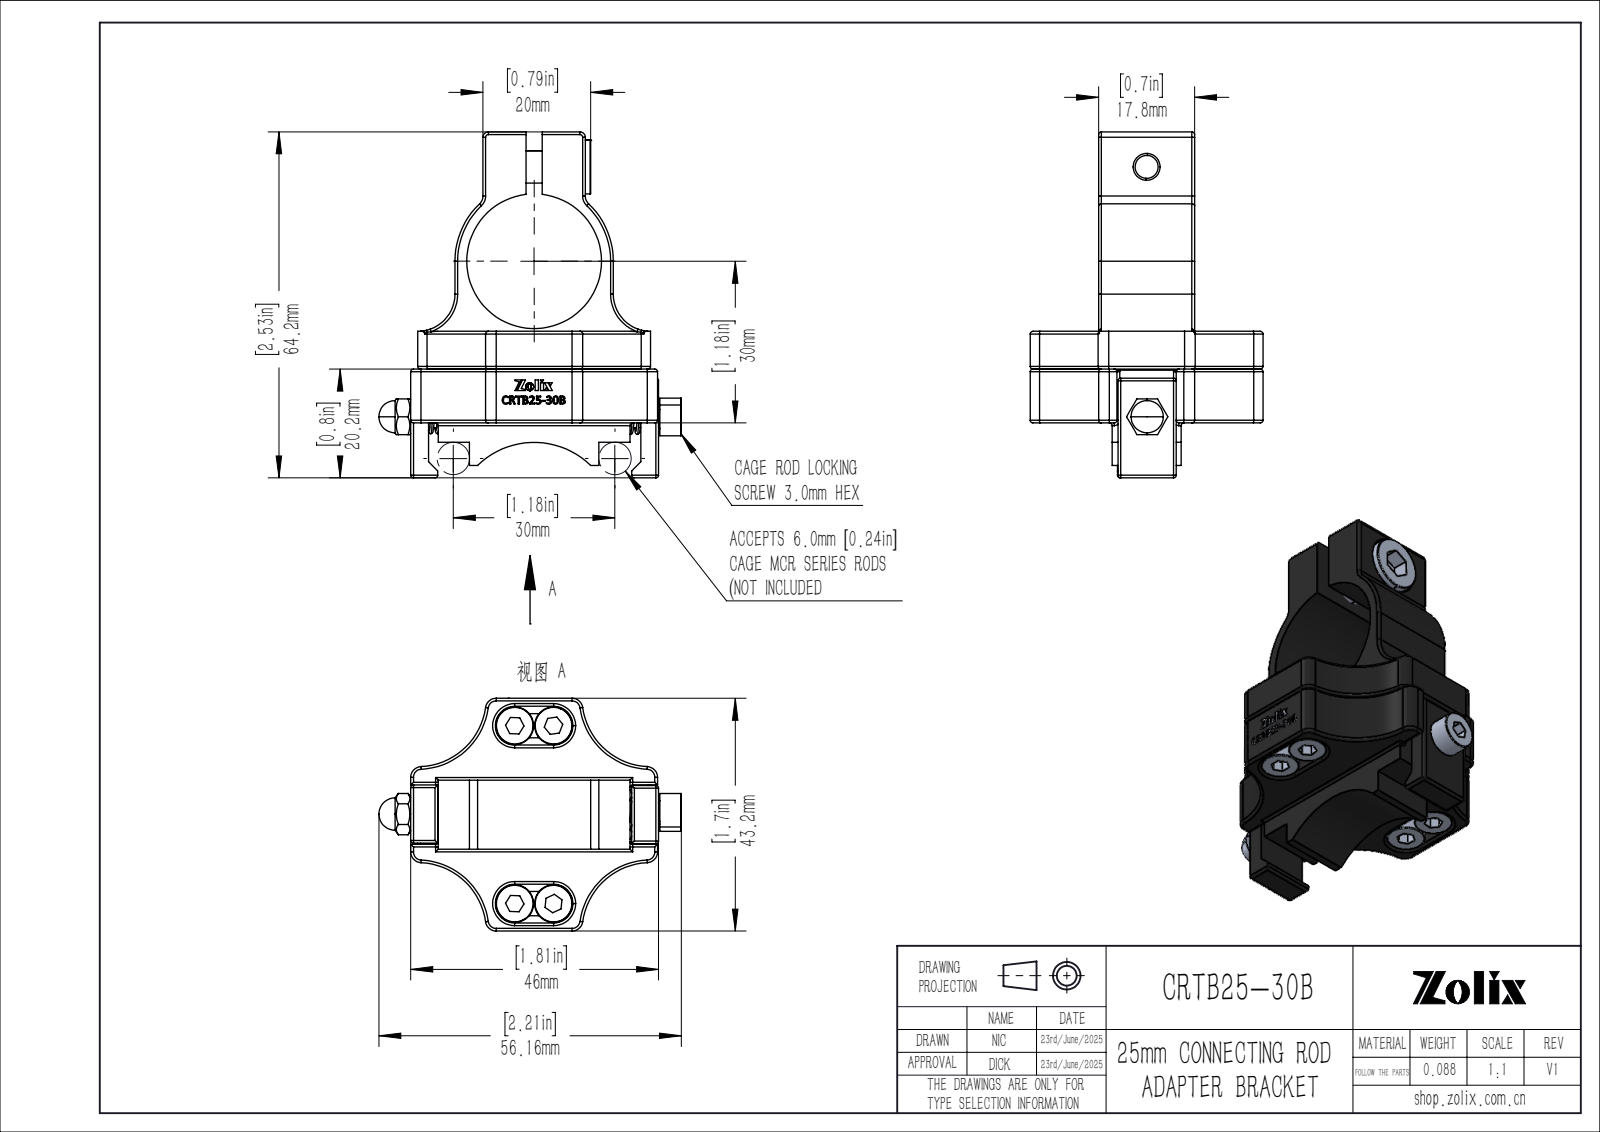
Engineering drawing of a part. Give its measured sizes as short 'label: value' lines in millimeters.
name: CRTB25-30B
written by: SolidWorks 2020 (CONFIG_CONTROL_DESIGN)
unit: mm
bodies: 13 solids, 864 faces (390 planar, 182 cylindrical, 292 other)
size: 64.2 × 56.16 × 43.2
volume: 32 580 mm³; area: 17 948 mm²
holes: 9× ⌀3.3, 1× ⌀4, 1× ⌀4.01, 1× ⌀4.4, 1× ⌀4.5, 1× ⌀5, 1× ⌀6.4, 1× ⌀6.5, 1× ⌀10.8, 1× ⌀25
bosses: 5× ⌀7, 5× ⌀4, 1× ⌀10, 1× ⌀6
rounds: 64× R0.5, 14× R2, 4× R2.25, 4× R3.6, 4× R12.7, 2× R1, 2× R6.9, 1× R14.7
face distances: 12.7, 7, 10, 17, 7.2, 2.5, 30.5, 15.3, 9.8, 17.8
hole spacings: 23.88, 7.2, 18.24, 28.43, 33, 33.78, 46.5, 46.34
